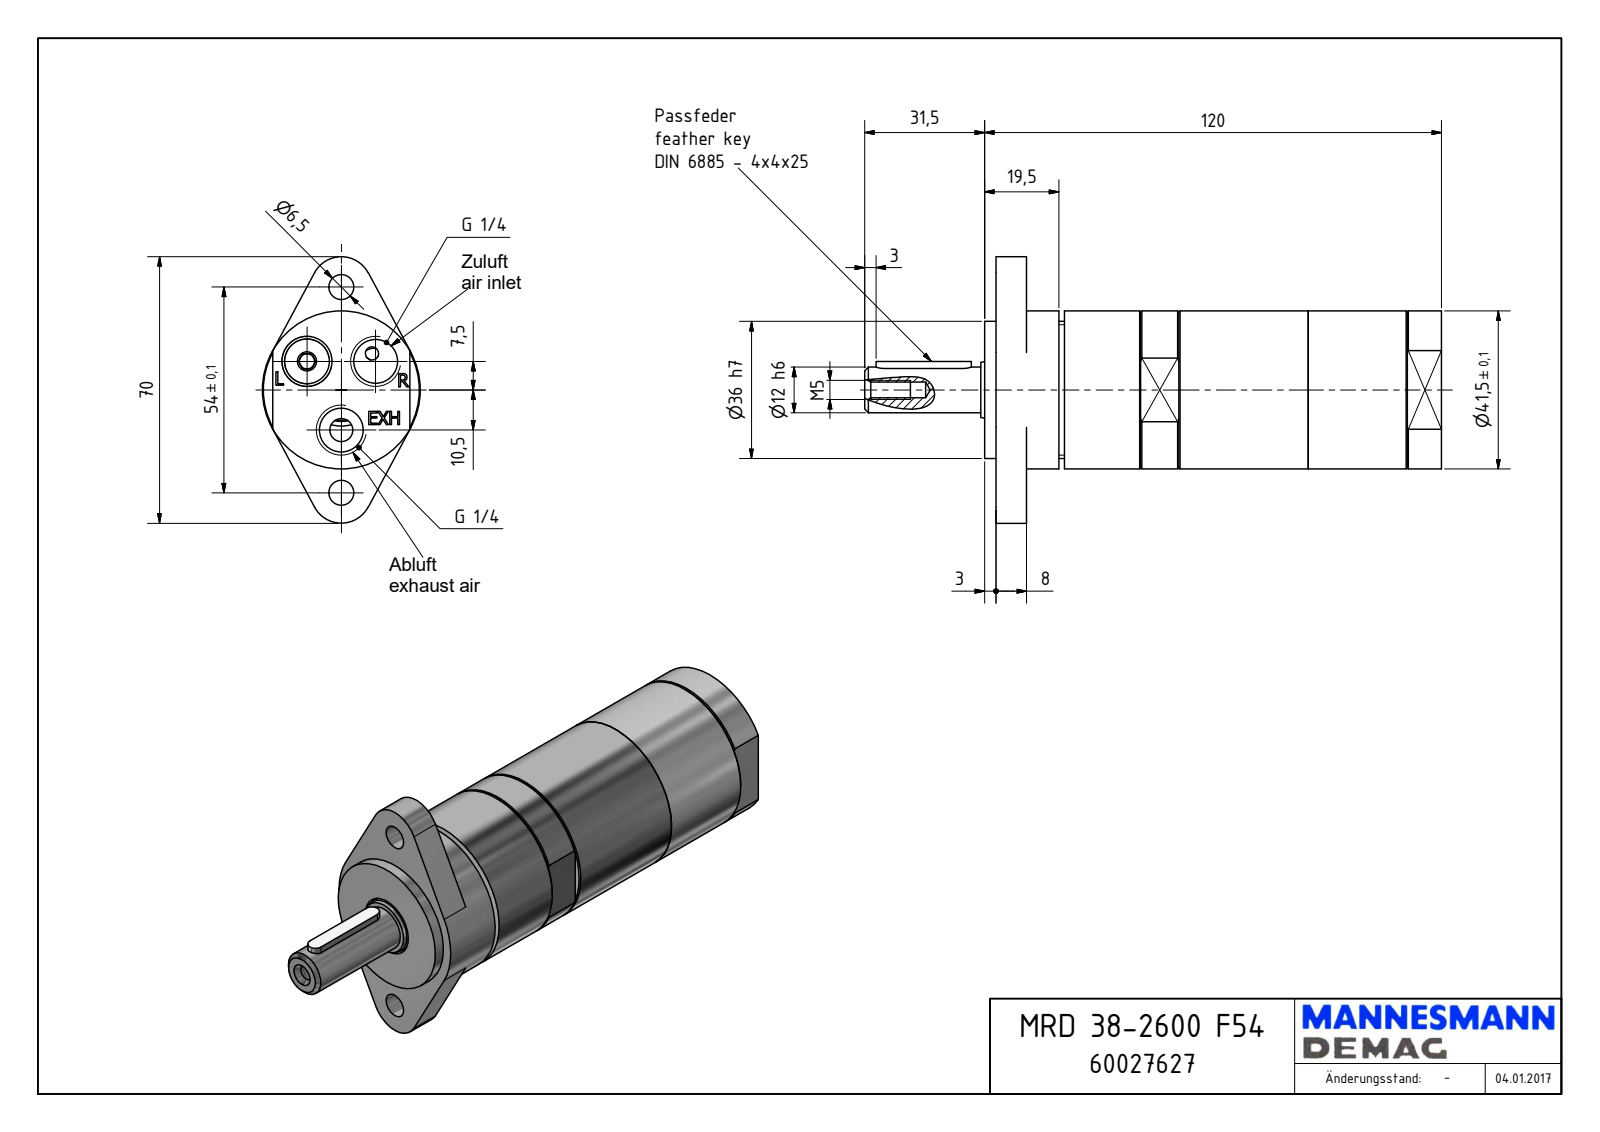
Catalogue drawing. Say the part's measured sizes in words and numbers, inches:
The part is named "MRD 38-2600 F54_60027627". Its 3-D file was written by "Autodesk Inventor 2018 (AUTOMOTIVE_DESIGN)". It is 1 solid with 153 faces: 103 planar, 24 cylindrical and 26 other. Overall it measures 5.965 by 2.756 by 1.634 inches. Its volume is 10.03 cubic inches and its surface area 36.43 square inches. Round holes: 3 of diameter 0.451, 2 of diameter 0.256, 1 of diameter 0.157, 1 of diameter 0.163, 1 of diameter 0.63. Round bosses or shafts: 1 of diameter 1.634, 1 of diameter 1.417, 1 of diameter 0.589, 1 of diameter 0.472. Partial cylindrical surfaces (rounded edges, fillets, slot ends): 2 of radius 0.079, 2 of radius 0.315. The main face-to-face distances are 4.606, 4.724, 0.118, 4.291, 0.315, 0.433, 0.394, 0.039, 3.898, 0.827. The hole center spacings are 0.461, 0.792, 0.846, 1.063, 1.404, 0.413, 0.65, 0.709.
